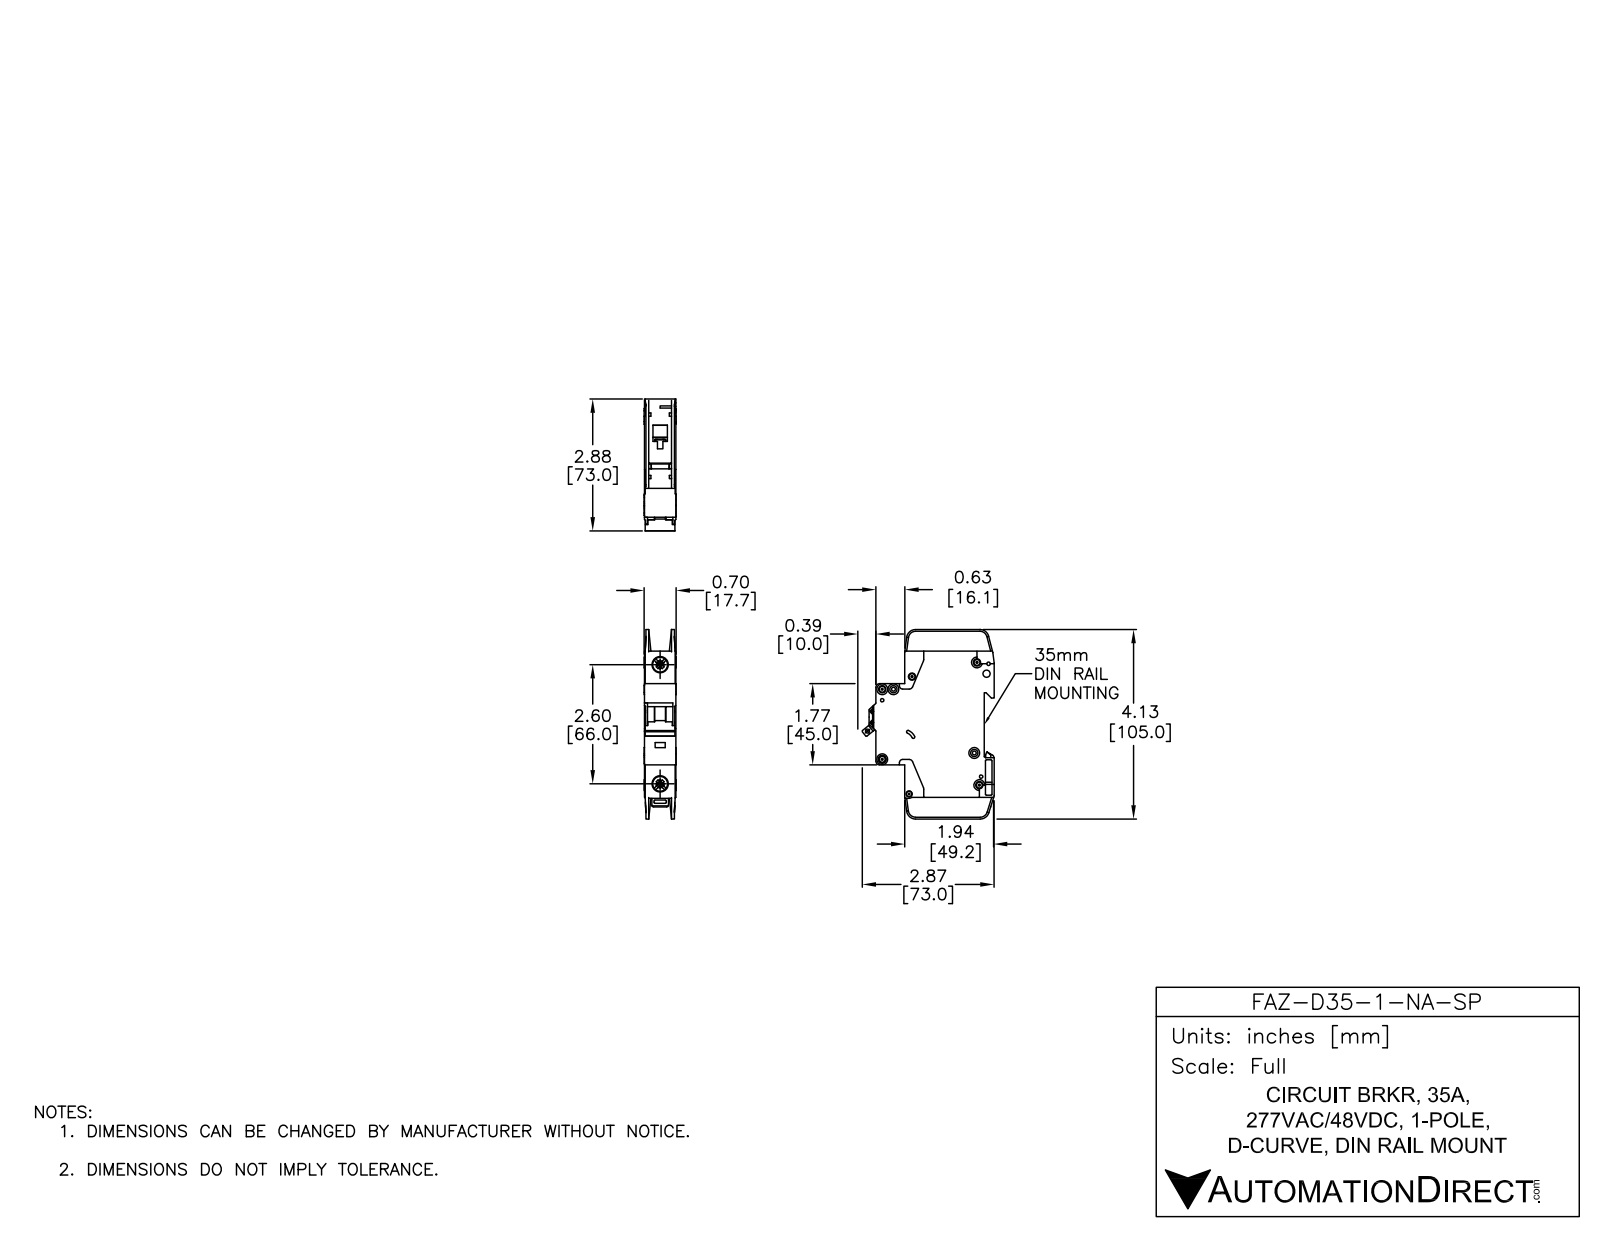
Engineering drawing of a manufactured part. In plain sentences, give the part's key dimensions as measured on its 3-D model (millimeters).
The part is named "FAZ-D35-1-NA-SP". Its 3-D file was written by "SolidWorks 2014 (AUTOMOTIVE_DESIGN)". It is 3 solids with 784 faces: 409 planar, 263 cylindrical and 112 other. Overall it measures 105 by 73.04 by 17.7 millimeters. Its volume is 77 695 cubic millimeters and its surface area 24 740 square millimeters. Round holes: 7 of diameter 3.6, 2 of diameter 1.09, 2 of diameter 1.5, 2 of diameter 4, 2 of diameter 7.15, 2 of diameter 8.2, 1 of diameter 1.9, 1 of diameter 2.15, 1 of diameter 2.2, 1 of diameter 2.55, 1 of diameter 3.3, 1 of diameter 3.4. Round bosses or shafts: 7 of diameter 6, 1 of diameter 2.5. Partial cylindrical surfaces (rounded edges, fillets, slot ends): 29 of radius 0.25, 18 of radius 0.5, 10 of radius 1, 10 of radius 2, 5 of radius 5, 4 of radius 4, 3 of radius 1.8, 2 of radius 0.2. The main face-to-face distances are 17.5, 15.05, 0.7, 2.45, 1.75, 15.75, 13.3, 14, 12.6, 2. The hole center spacings are 6.2, 5.19, 6.1, 8.19, 8.56, 8.7, 11.11, 12.45.
